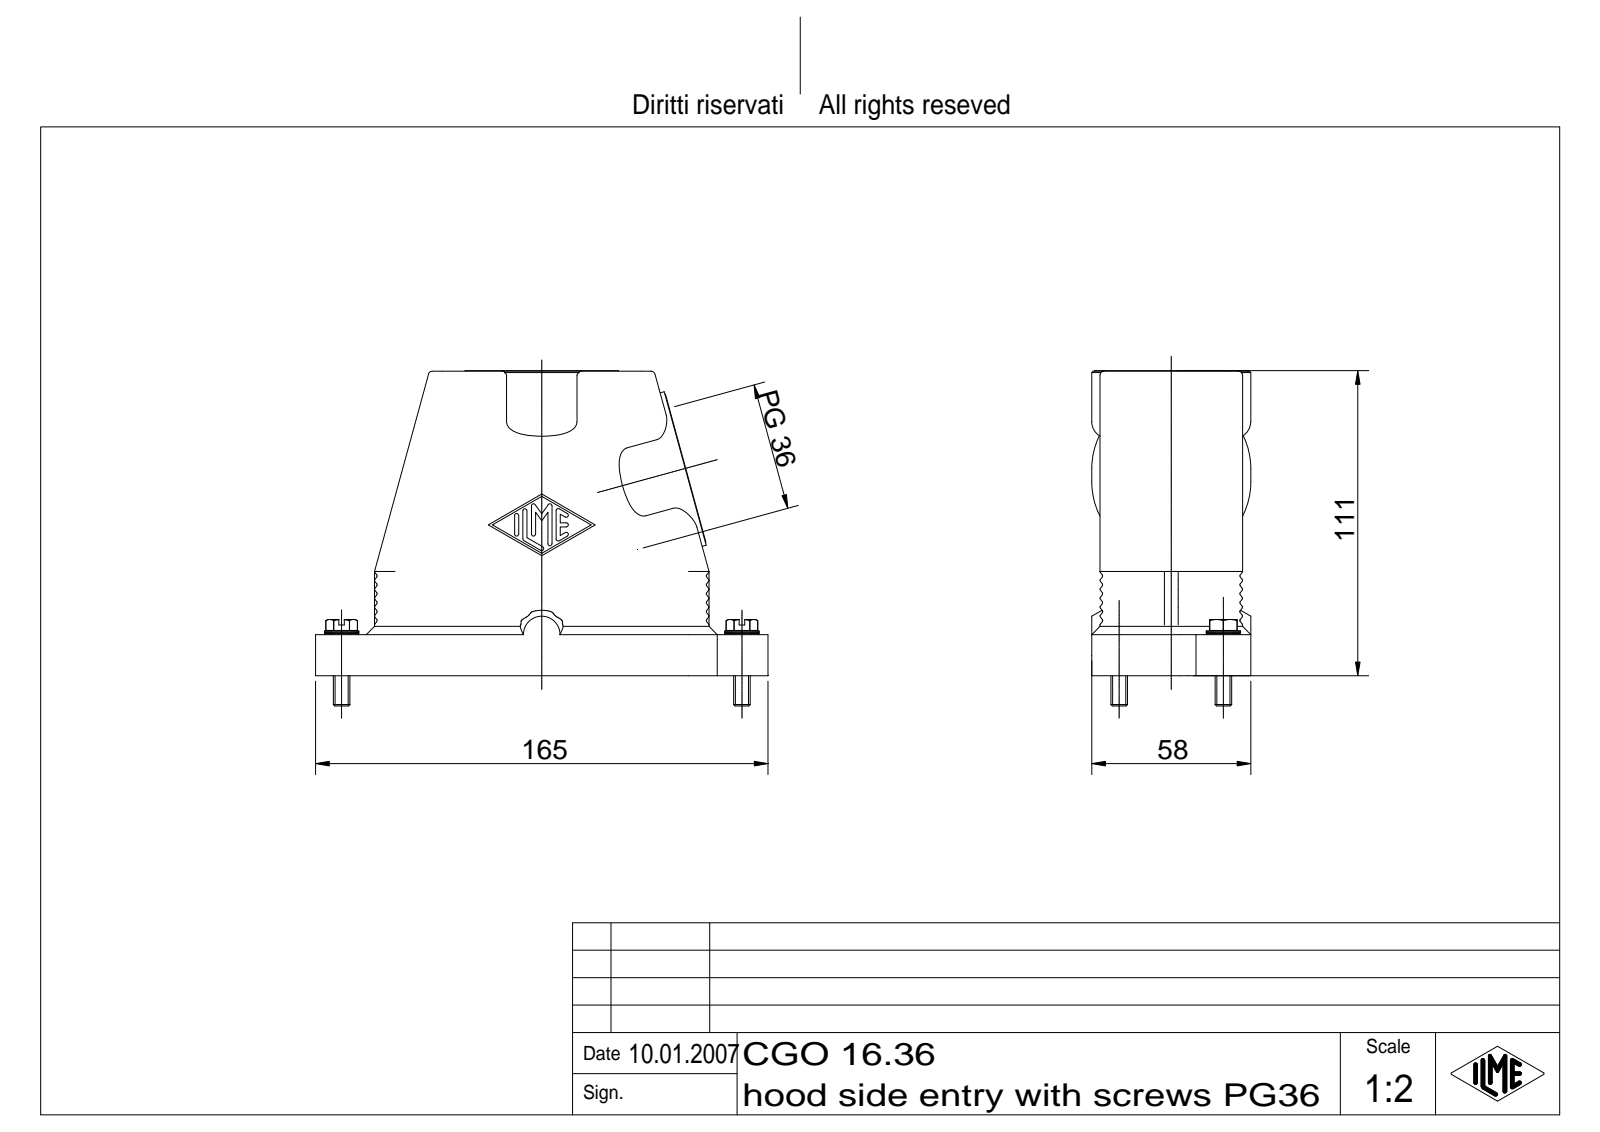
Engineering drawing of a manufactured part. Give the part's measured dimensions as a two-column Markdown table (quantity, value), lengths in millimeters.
| quantity | value |
| --- | --- |
| part name | CGO 16.36 |
| STEP written by | Autodesk Inventor 7 (AUTOMOTIVE_DESIGN) |
| units | millimeters |
| bodies | 3 solids, 768 faces (190 planar, 195 cylindrical, 383 other) |
| overall size | 165 × 122.2 × 58 |
| volume | 212 219 mm³ |
| surface area | 91 032 mm² |
| round holes (diameter × count) | 2.46 × 2, 3.2 × 2, 6.6 × 2, 15 × 2, 45.48 × 1 |
| round bosses / shafts (diameter × count) | 58 × 2, 56 × 2, 12.5 × 2, 6 × 2 |
| partial cylindrical surfaces (radius × count) | 0.5 × 39, 0.75 × 14, 7.5 × 8, 6 × 6, 1.5 × 4, 3 × 4, 5.75 × 2, 10.5 × 2 |
| main face-to-face distances | 3, 52, 49, 6, 46, 55, 2.5, 0.5, 58, 3.5 |
| hole center spacings | 34.69, 116.38, 82.07, 150.86 |
